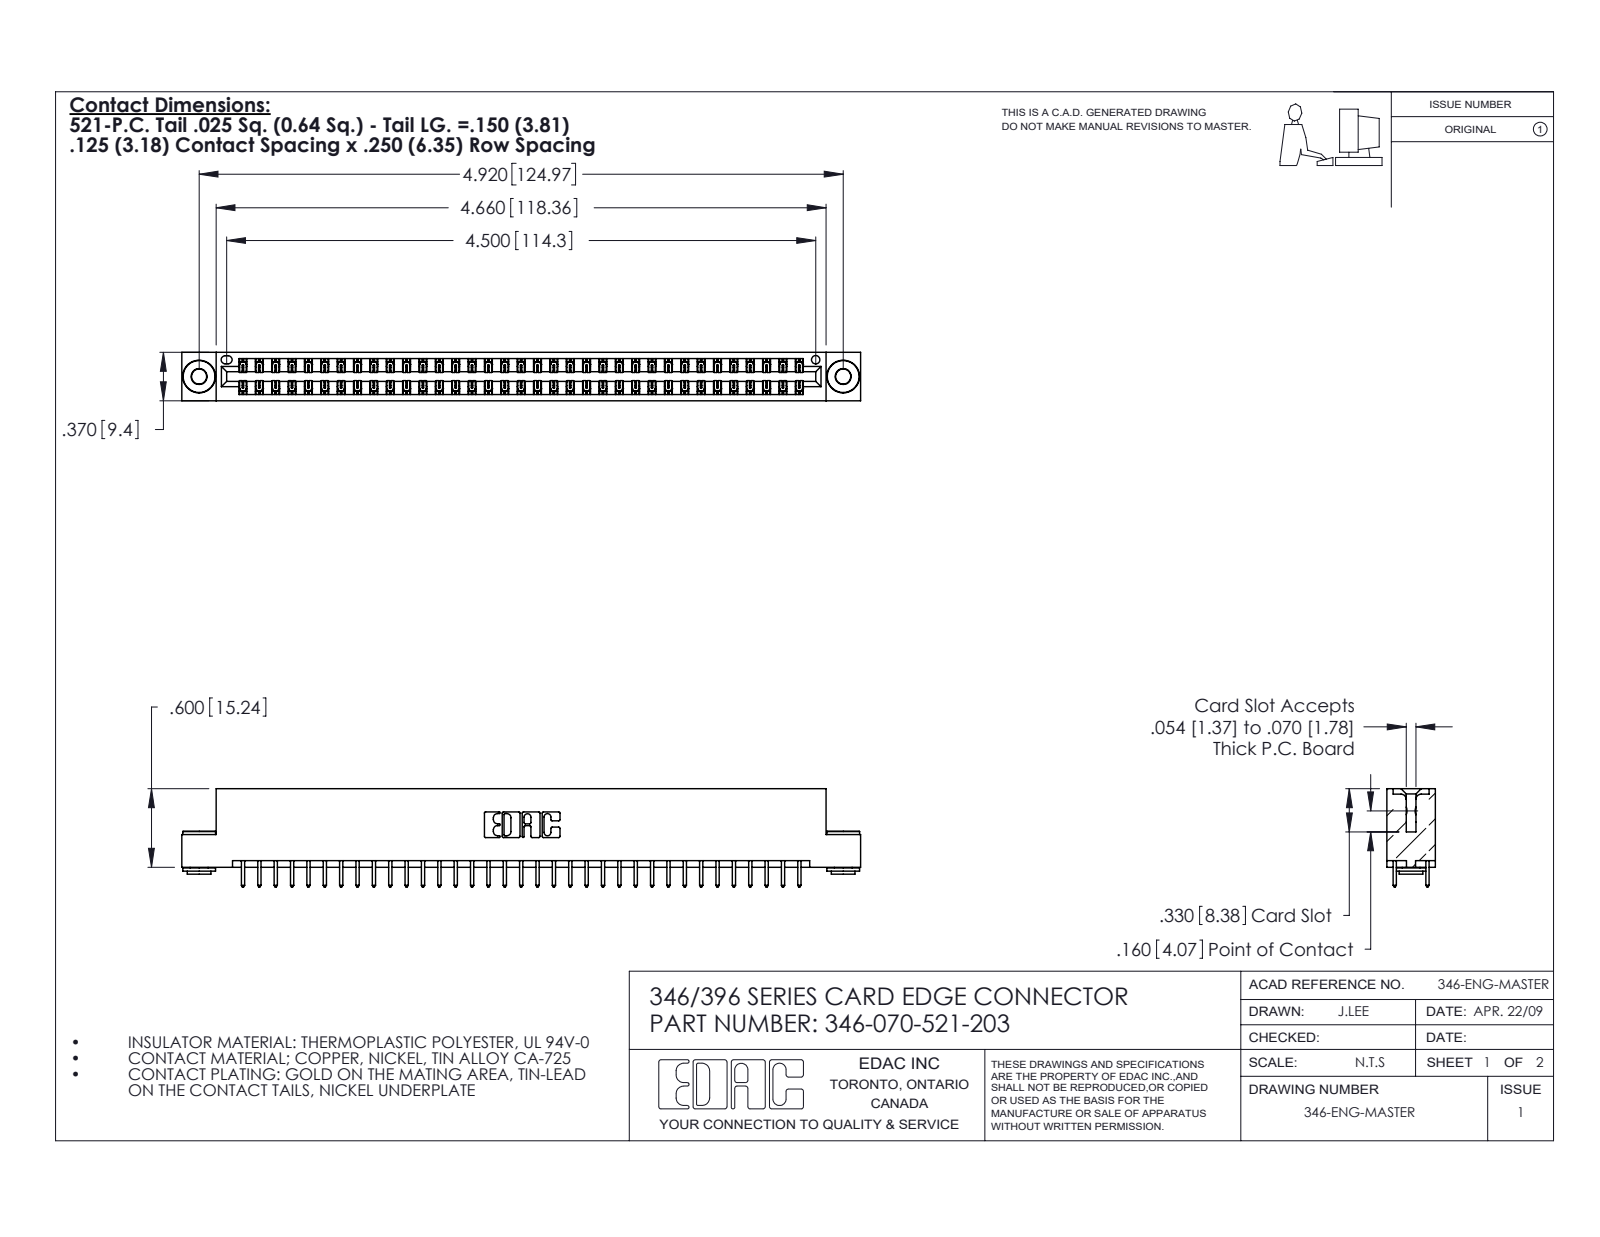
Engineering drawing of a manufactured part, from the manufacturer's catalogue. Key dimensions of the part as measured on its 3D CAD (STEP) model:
Part name (STEP PRODUCT): 345-250-002_345-250-002-102; 346-070-521-203; 345-292-001_345-293-121; 346 Part_Flush Mounting Lugs - 0.156 Dia-TH
STEP written by: SolidWorks 2020 (CONFIG_CONTROL_DESIGN)
Units: inches
Bodies: 73 solids, 3814 faces (2550 planar, 1256 cylindrical, 8 other)
Overall size (bounding box): 5.185 × 0.75 × 0.37
Volume: 0.779 in³ · Surface area: 27.1 in²
Round holes (diameter × count): ⌀0.116 ×2, ⌀0.156 ×2, ⌀0.064 ×1
Round bosses / shafts (diameter × count): ⌀0.25 ×2, ⌀0.18 ×2, ⌀0.136 ×2
Partial cylindrical surfaces — rounded edges, fillets, slot ends (radius × count): R0.006 ×105, R0.01 ×70, R0.01 ×22, R0.007 ×6, R0.031 ×6, R0.026 ×3, R0.014 ×2, R0.022 ×2
Main face-to-face distances: 0.048, 0.322, 0.25, 0.37, 0.025, 0.072, 0.298, 0.275, 0.148, 0.222
Hole centre spacings: 0.246, 4.711, 4.92
